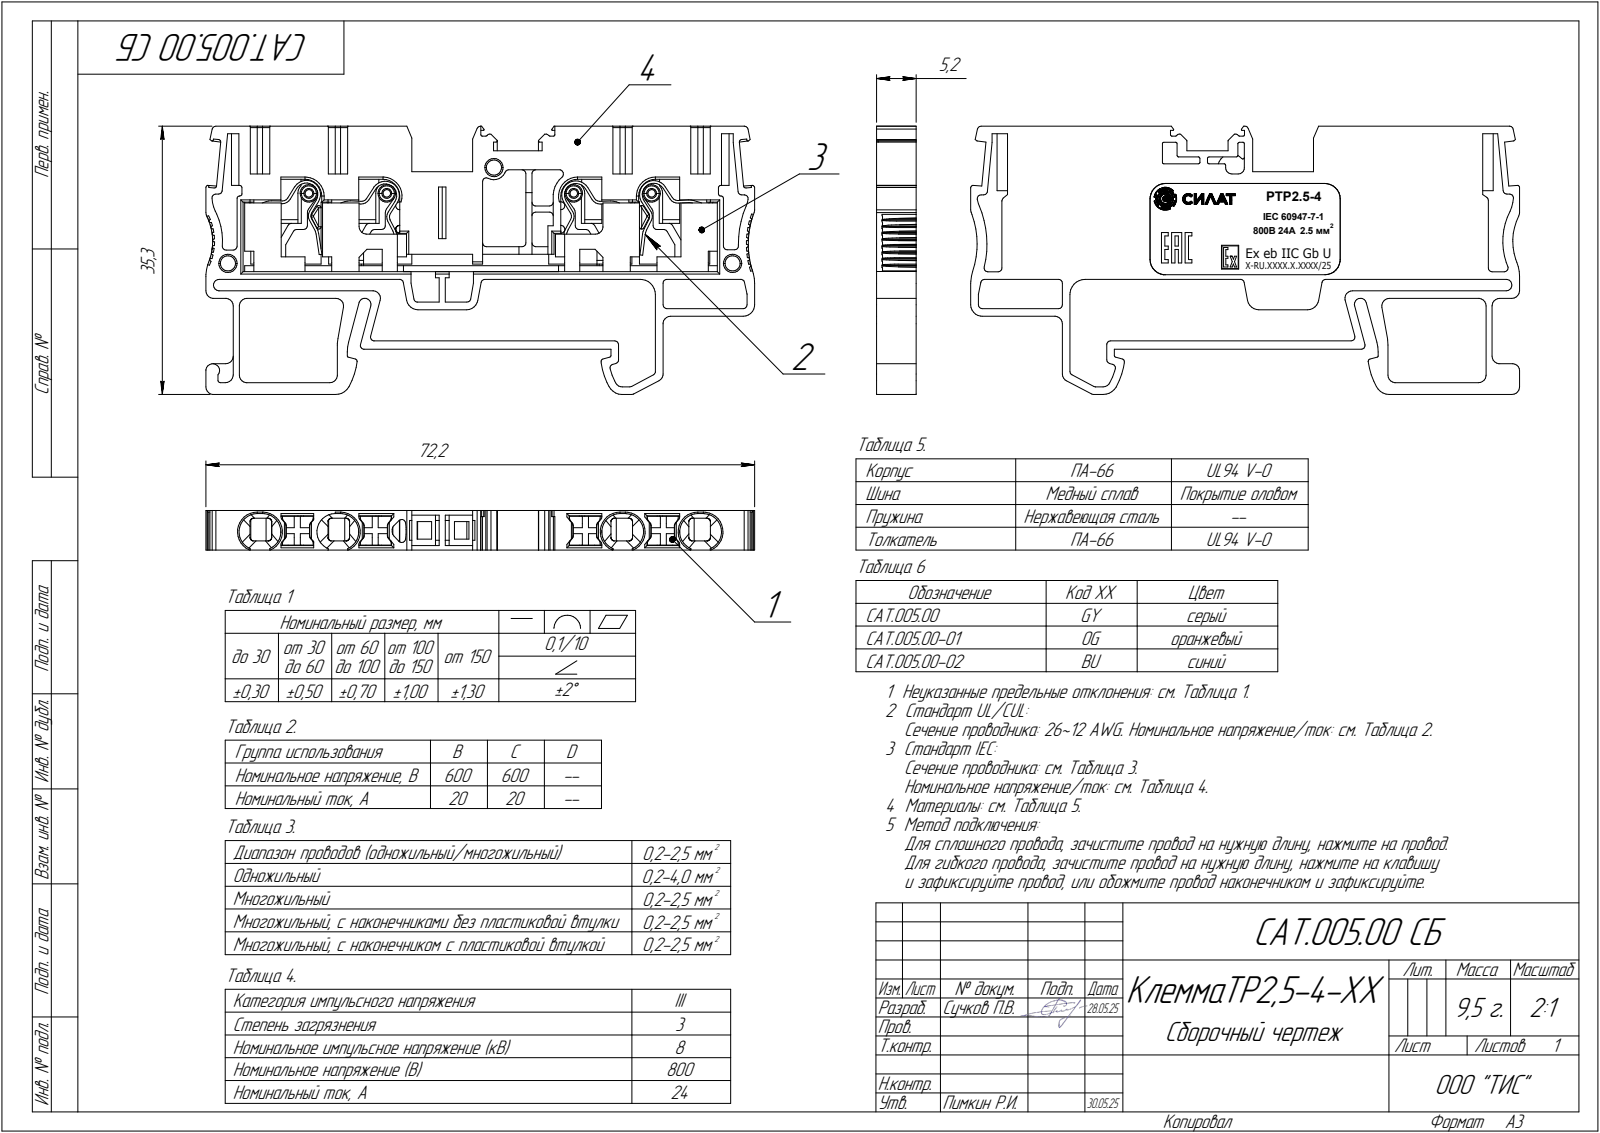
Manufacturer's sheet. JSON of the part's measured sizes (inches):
{"part_name": "Клемма PTP2,5-4-XX", "step_written_by": "SolidWorks 2024 (AUTOMOTIVE_DESIGN)", "units": "inches", "bodies": {"solids": 1, "faces": 446, "planar": 296, "cylindrical": 140, "other": 10}, "overall_size": [2.843, 1.39, 0.205], "volume_in3": 0.581, "surface_area_in2": 9.114, "partial_cylinders_radius": [[0.02, 41], [0.012, 36], [0.039, 12], [0.094, 8], [0.006, 7], [0.008, 6], [0.197, 5], [0.004, 2]], "face_to_face_distances": [0.205, 0.173, 1.156, 0.234, 1.39, 1.207, 0.973, 0.183, 0.498, 0.264]}
